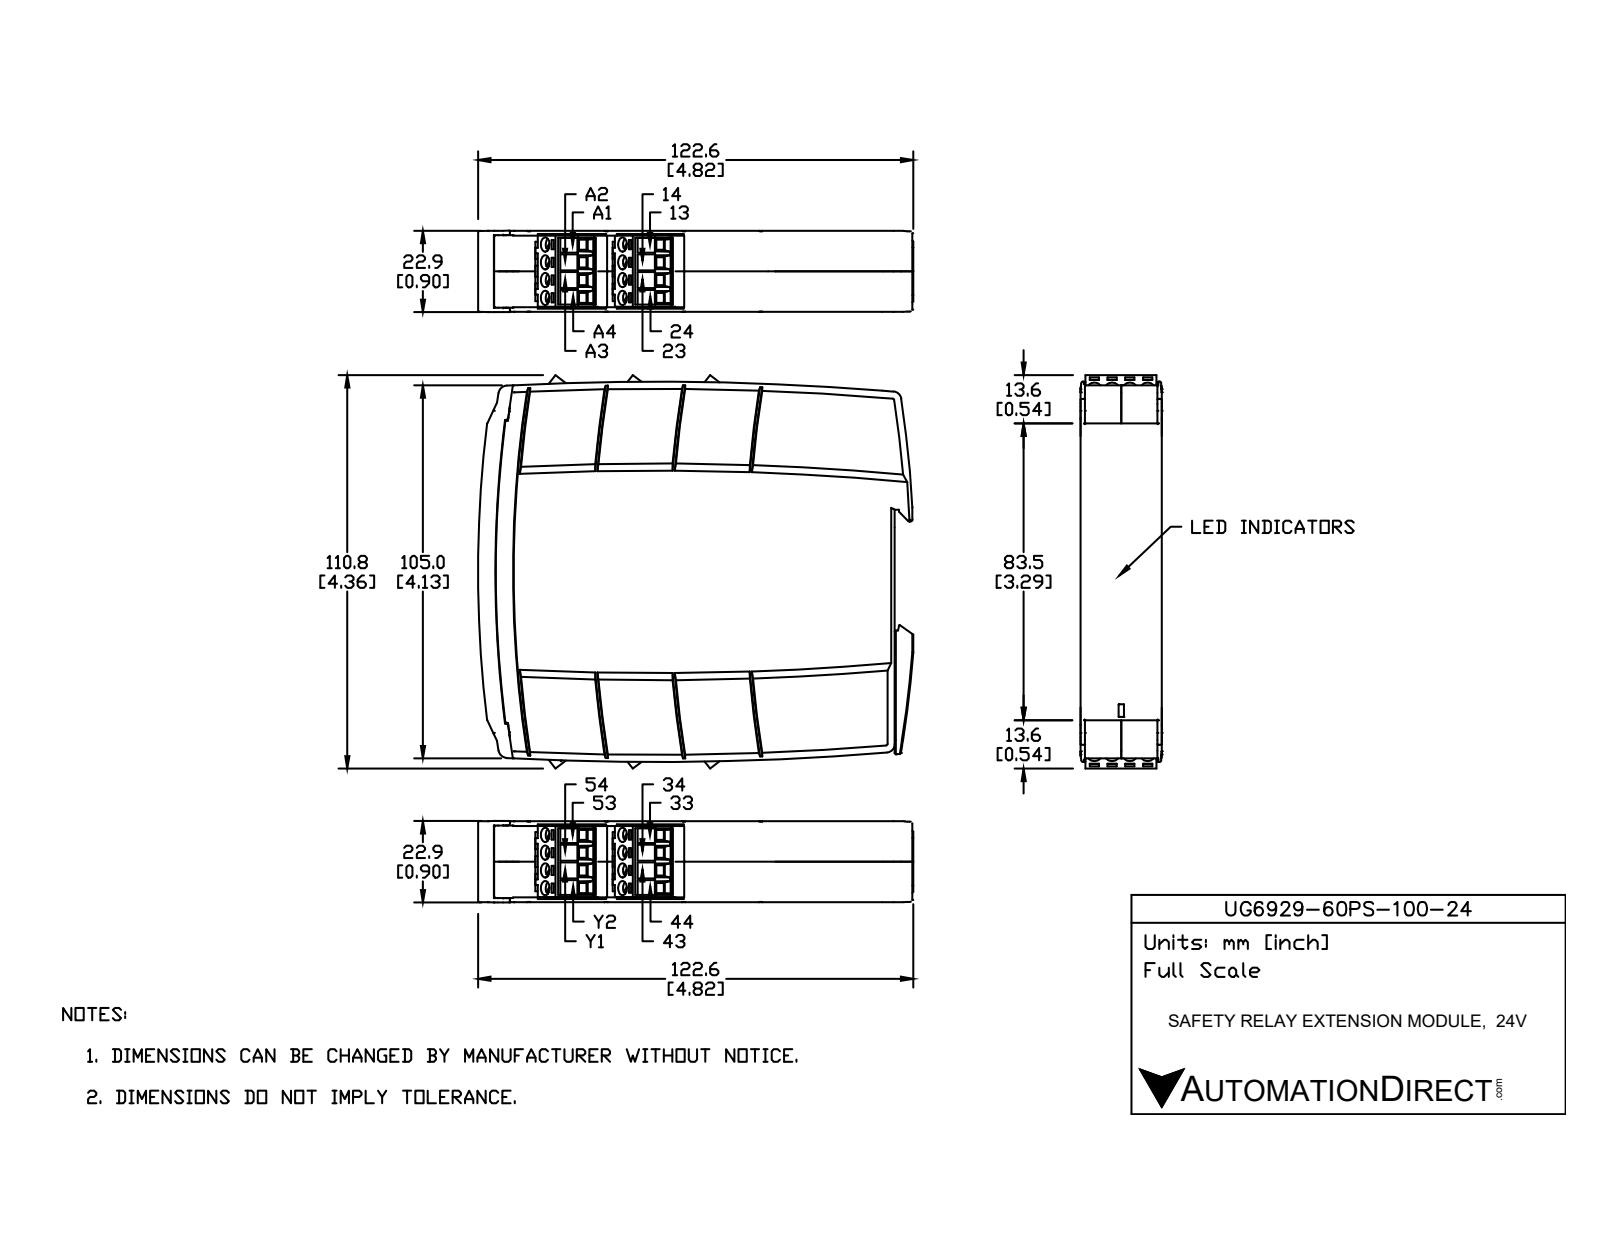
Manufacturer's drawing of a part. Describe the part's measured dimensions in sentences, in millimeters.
The part is named "UG6929-60PS-100-24". Its 3-D file was written by "SolidWorks 2021 (AUTOMOTIVE_DESIGN)". It is 1 solid with 521 faces: 437 planar, 83 cylindrical and 1 other. Overall it measures 119.2 by 110.6 by 22.5 millimeters. Its volume is 264 300 cubic millimeters and its surface area 36 910 square millimeters. Round holes: 16 of diameter 4, 1 of diameter 1.3. Round bosses or shafts: 1 of diameter 1.2. Partial cylindrical surfaces (rounded edges, fillets, slot ends): 12 of radius 0.1, 8 of radius 0.3, 7 of radius 2.4, 6 of radius 0.1, 4 of radius 0.1, 4 of radius 800, 3 of radius 0.5, 2 of radius 0.3. The main face-to-face distances are 22.5, 1.2, 21.3, 111.2, 13.4, 17.1, 20, 105.4, 8.8, 1.1. The hole center spacings are 5, 14.3, 10, 13.4, 16.7, 15, 20.1.
